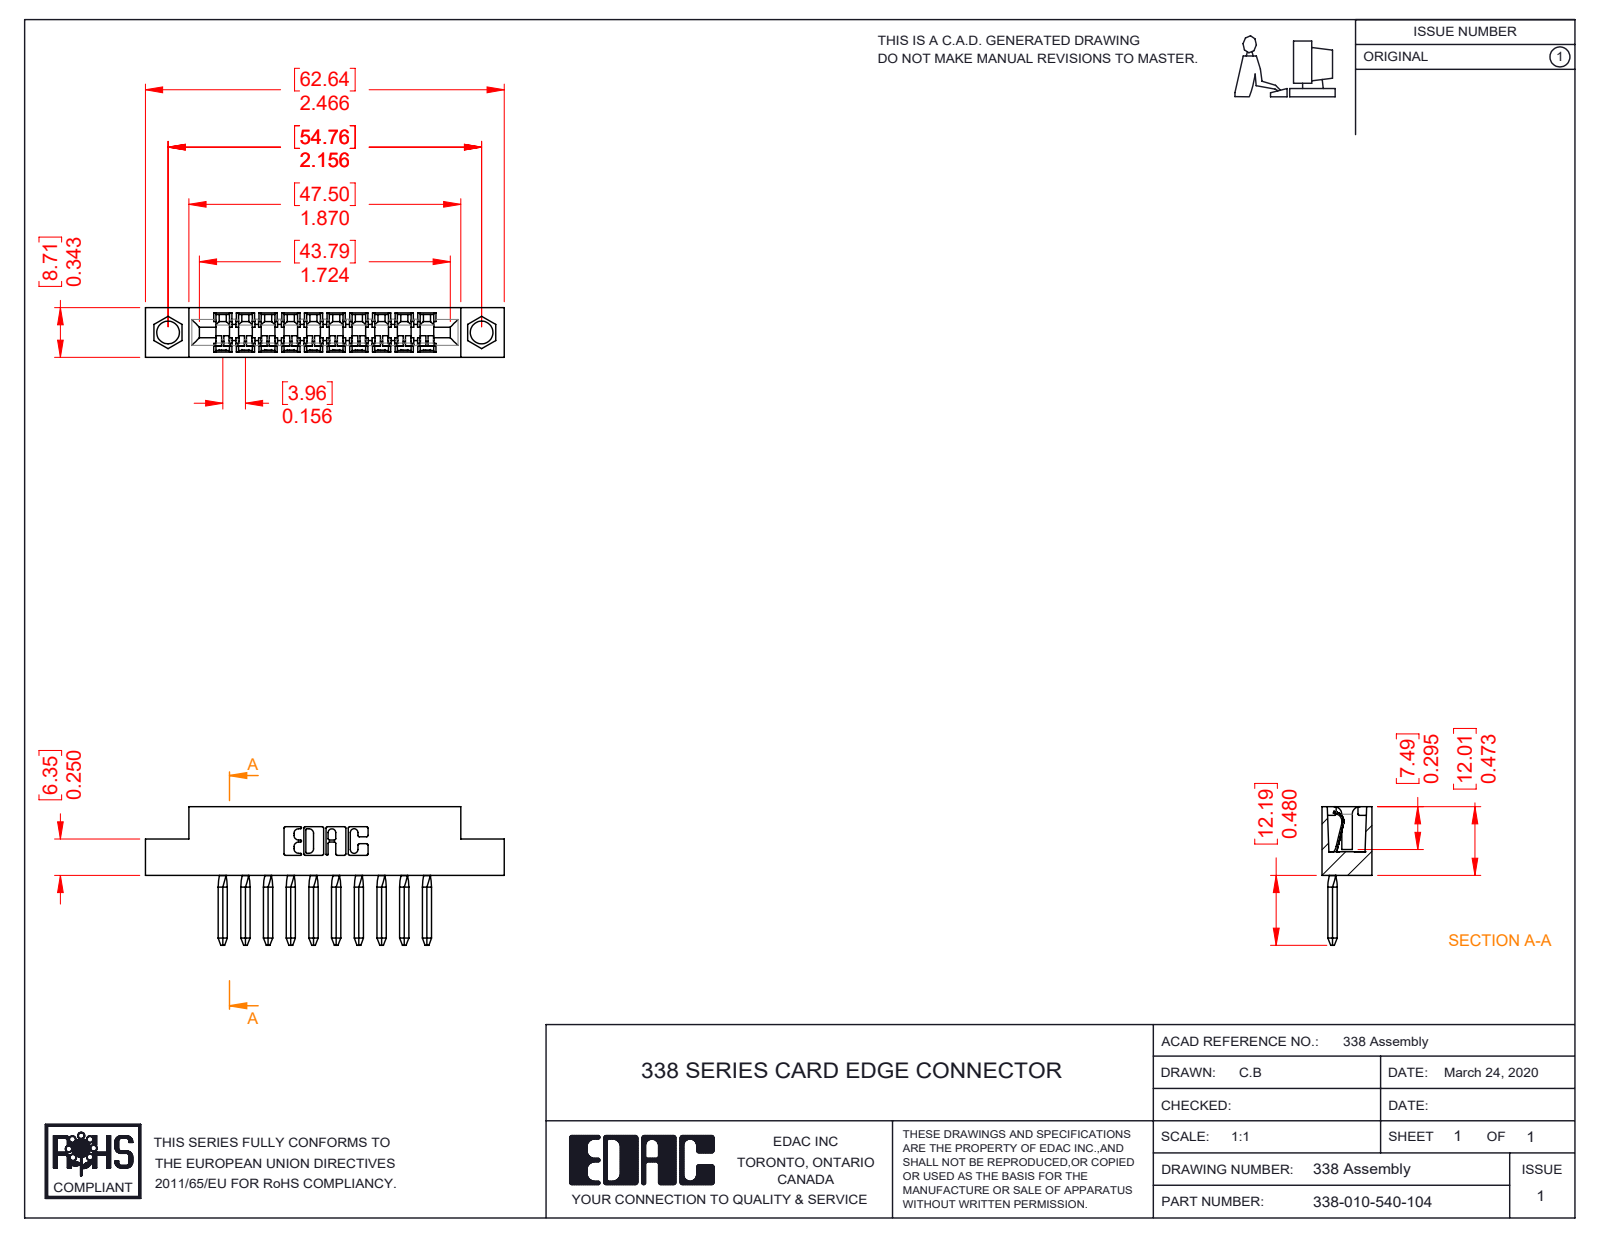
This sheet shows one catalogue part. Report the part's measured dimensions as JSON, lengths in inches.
{"part_name": "338-210-001_338-210-010-004; 338-010-540-104; 338-290-001_540", "step_written_by": "SolidWorks 2016 (CONFIG_CONTROL_DESIGN)", "units": "inches", "bodies": {"solids": 11, "faces": 1038, "planar": 714, "cylindrical": 284, "other": 40}, "overall_size": [2.466, 0.953, 0.343], "volume_in3": 0.253, "surface_area_in2": 9.11, "round_holes": [[0.156, 2]], "partial_cylinders_radius": [[0.025, 42], [0.01, 22], [0.007, 10], [0.055, 8], [0.067, 8], [0.1, 8], [0.007, 6], [0.031, 6]], "face_to_face_distances": [0.343, 0.156, 0.25, 0.624, 0.468, 0.312, 0.312, 0.045, 0.11, 0.78], "hole_center_spacings": [2.156]}
